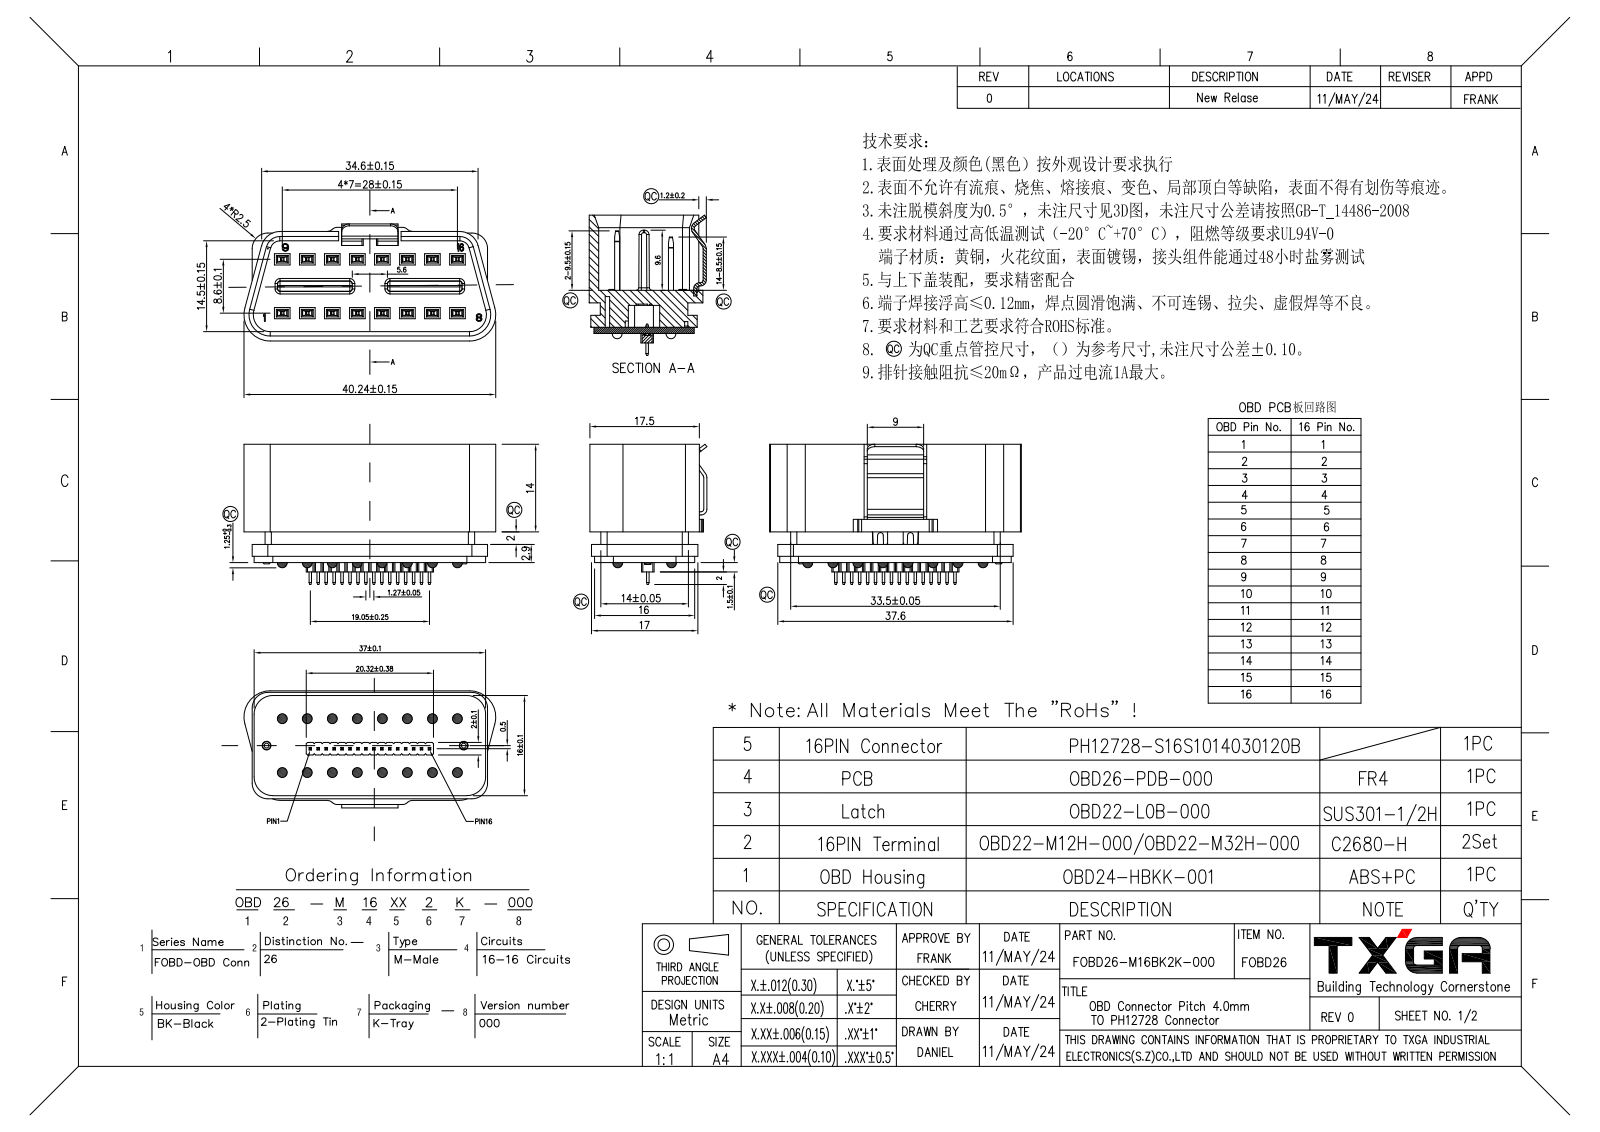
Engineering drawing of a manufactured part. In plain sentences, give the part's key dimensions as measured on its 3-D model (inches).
The part is named "HOUSING22337046TUX; PIN9; WAN-PIN37046TUX; PCB22337046TUX (+5 more)". Its 3-D file was written by "PRO/ENGINEER BY PARAMETRIC TECHNOLOGY CORPORATION, 2010280 (CONFIG_CONTROL_DESIGN)". It is 92 solids with 2826 faces: 2359 planar, 443 cylindrical and 24 other. Overall it measures 1.584 by 0.882 by 0.736 inches. Its volume is 0.341 cubic inches and its surface area 15.22 square inches. Round holes: 16 of diameter 0.026, 16 of diameter 0.047, 2 of diameter 0.055, 1 of diameter 0.098. Round bosses or shafts: 16 of diameter 0.063, 2 of diameter 0.051. Partial cylindrical surfaces (rounded edges, fillets, slot ends): 64 of radius 0.004, 36 of radius 0.006, 32 of radius 0.008, 21 of radius 0.016, 12 of radius 0.039, 6 of radius 0.012, 6 of radius 0.118, 4 of radius 0.02. The main face-to-face distances are 0.059, 0.031, 0.63, 0.039, 0.53, 0.1, 0.157, 0.272, 0.159, 0.232. The hole center spacings are 0.157, 0.373, 0.315, 0.463, 0.581, 0.472, 0.339, 0.63.
